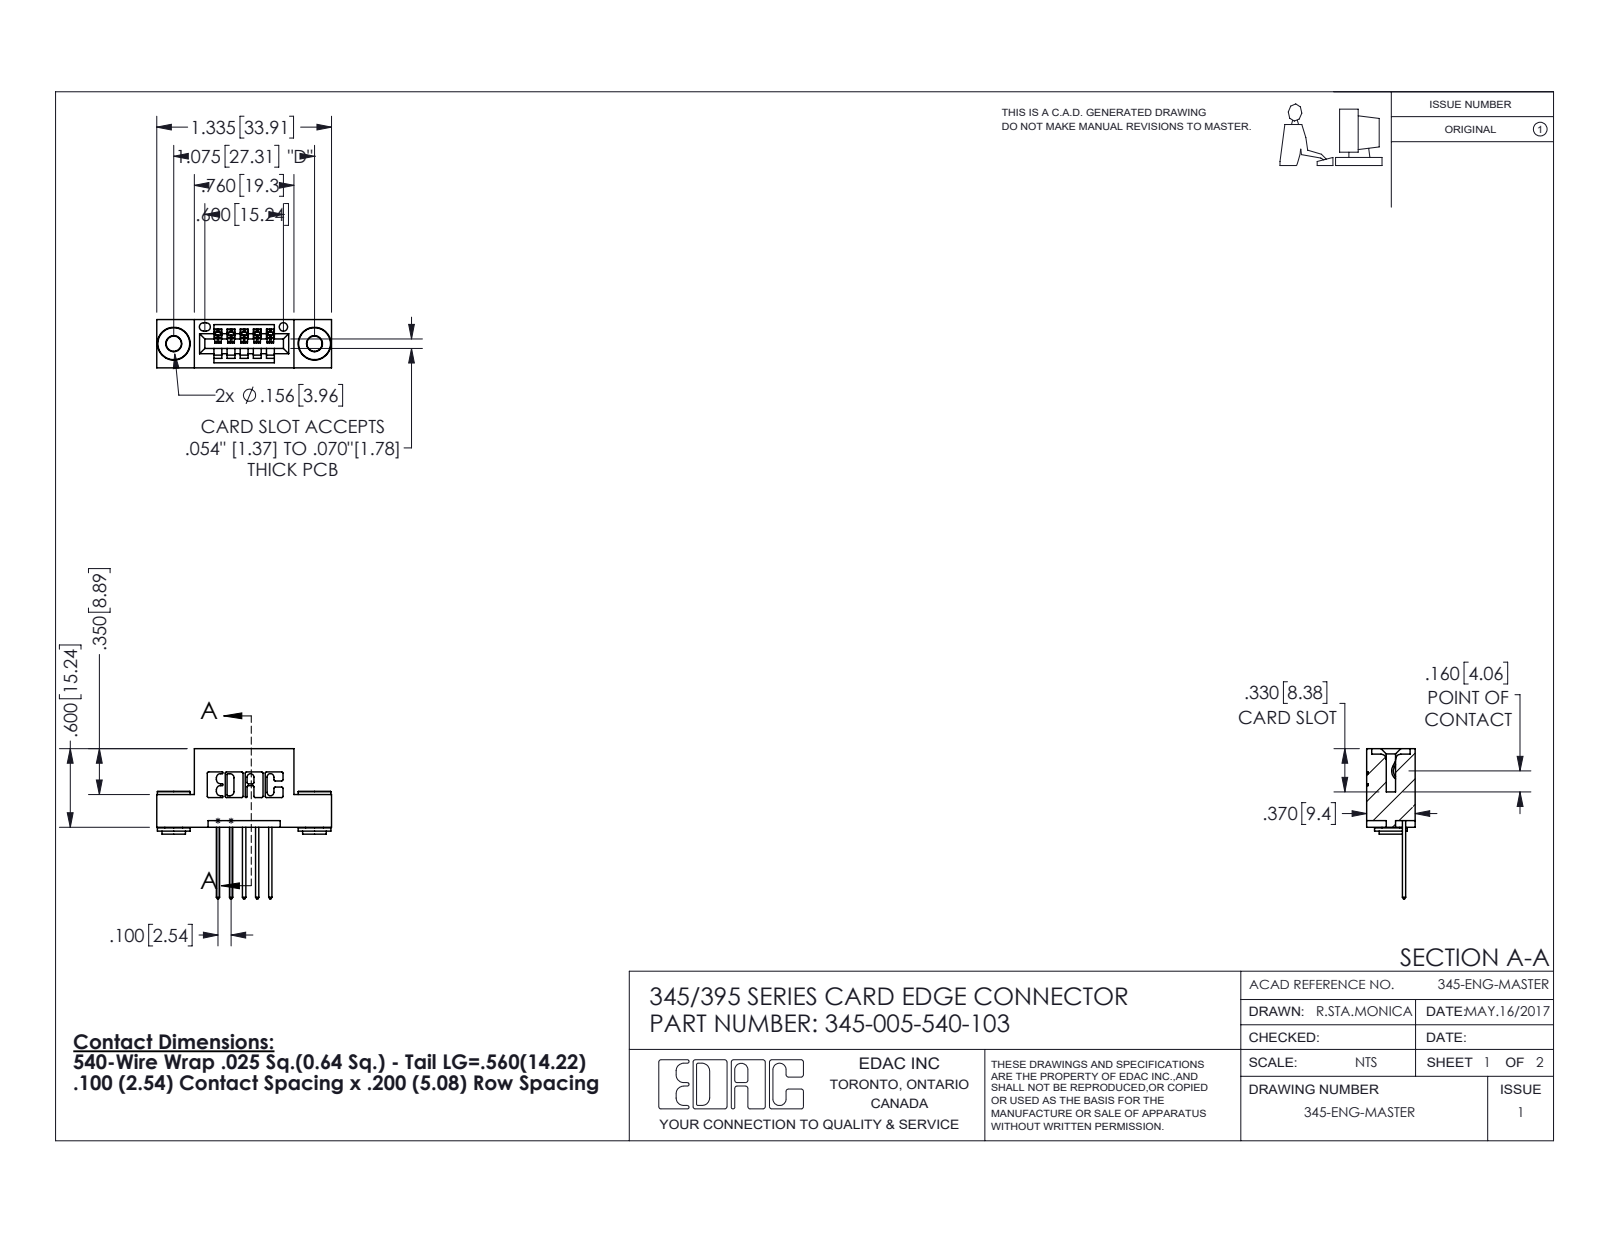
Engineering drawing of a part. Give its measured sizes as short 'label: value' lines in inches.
name: 345-005-540-103; 345-250-002_345-250-002-102; 345 Part_Flush Mounting Lugs - 0.156 Dia-TH; 345-292-001_345-293-140
written by: SolidWorks 2016 (CONFIG_CONTROL_DESIGN)
unit: in
bodies: 8 solids, 454 faces (290 planar, 156 cylindrical, 8 other)
size: 1.335 × 1.147 × 0.37
volume: 0.18 in³; area: 5.692 in²
holes: 2× ⌀0.116, 2× ⌀0.156, 1× ⌀0.064
bosses: 2× ⌀0.25, 2× ⌀0.18, 2× ⌀0.136
rounds: 22× R0.01, 10× R0.006, 10× R0.01, 6× R0.007, 6× R0.031, 3× R0.026, 2× R0.031, 2× R0.04
face distances: 0.2, 0.37, 0.072, 0.298, 0.1, 0.025, 0.25, 0.098, 0.272, 0.06
hole spacings: 0.27, 0.847, 1.075
